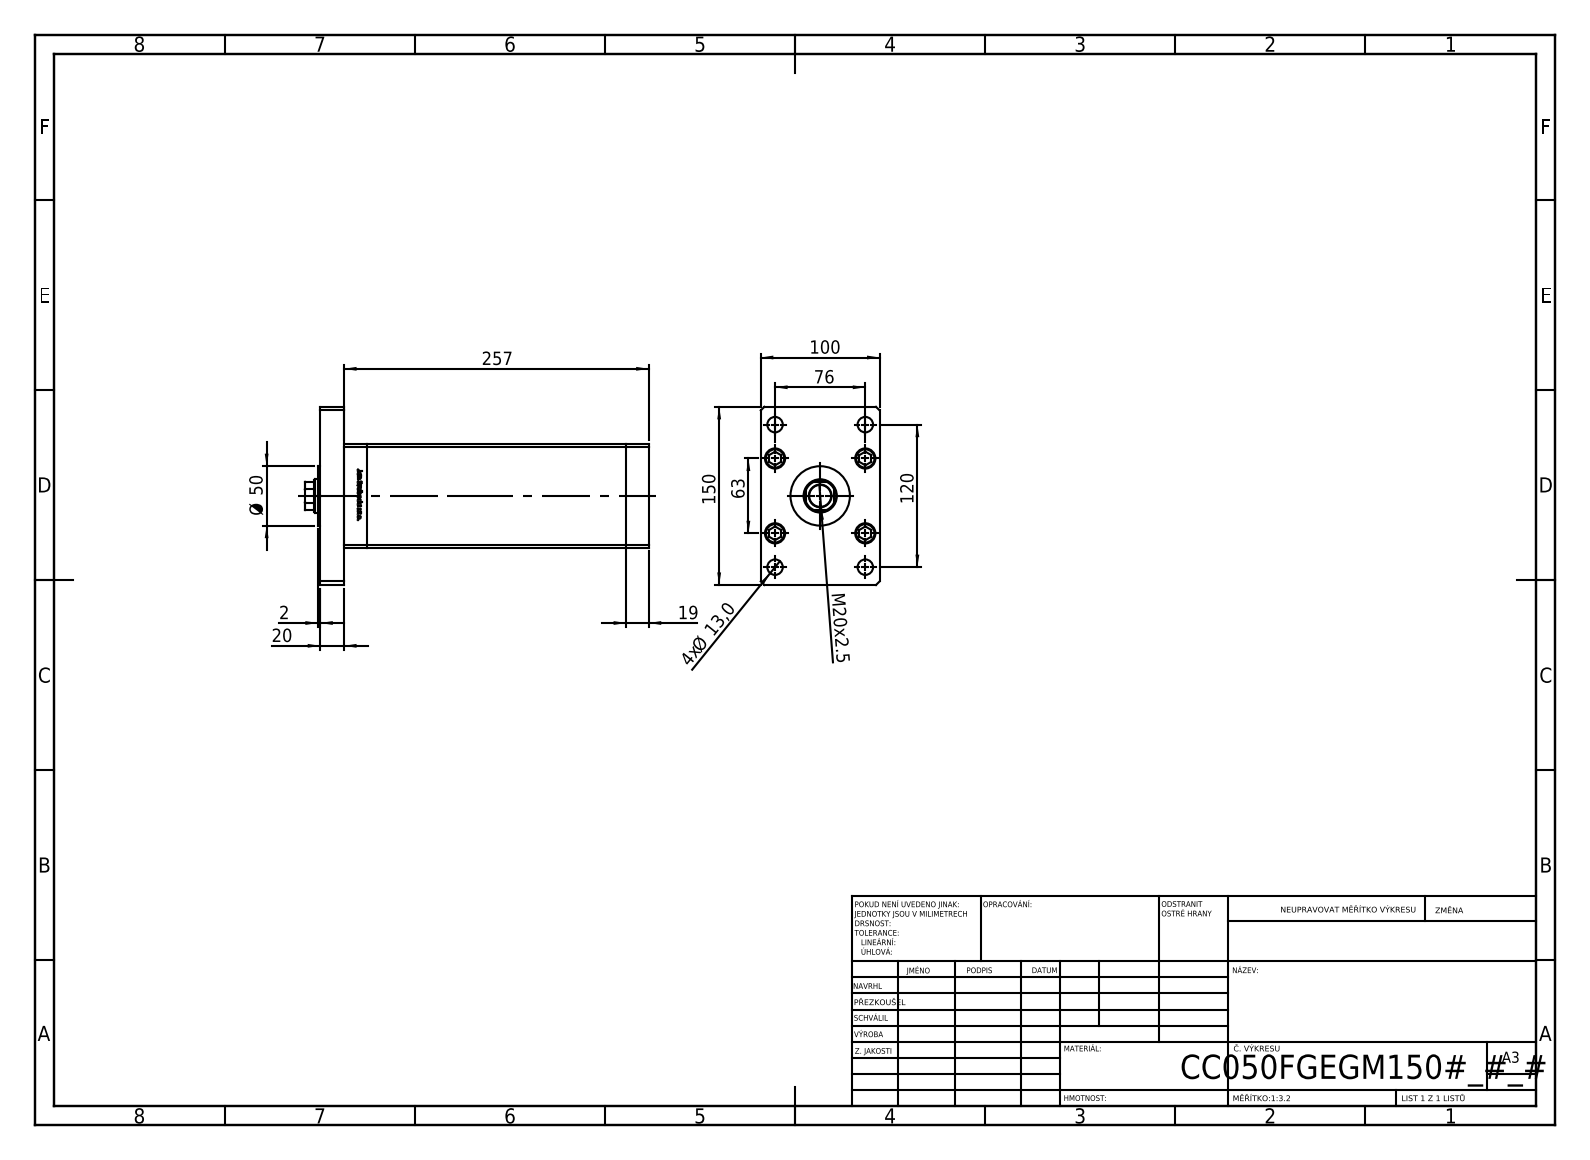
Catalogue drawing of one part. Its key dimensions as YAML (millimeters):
part_name: "V220C_FRONT_F; V220C BACK_F; V220C_VC_F; V220C_F (+2 more)"
step_written_by: "SolidWorks 2019 (CONFIG_CONTROL_DESIGN)"
units: millimeters
bodies: {solids: 19, faces: 1311, planar: 517, cylindrical: 188, other: 606}
overall_size: [289.5, 150, 100]
volume: 2205000
surface_area: 304087
round_holes:
  - {diameter: 13.5, count: 7}
  - {diameter: 18, count: 7}
  - {diameter: 12, count: 4}
  - {diameter: 13, count: 4}
  - {diameter: 17, count: 4}
  - {diameter: 2, count: 2}
  - {diameter: 13.16, count: 2}
  - {diameter: 18.5, count: 1}
  - {diameter: 28, count: 1}
  - {diameter: 29.5, count: 1}
round_bosses_or_shafts:
  - {diameter: 8, count: 9}
  - {diameter: 17, count: 5}
  - {diameter: 50, count: 1}
partial_cylinders:
  - {radius: 0.93, count: 2}
  - {radius: 13.5, count: 1}
face_to_face_distances: [100, 87, 19, 237.5, 20, 218.5, 39, 257.5, 256.5, 276.5]
hole_center_spacings: [34, 18.59, 28.5, 37.13, 39.64, 49.36, 57.95, 71.02]
